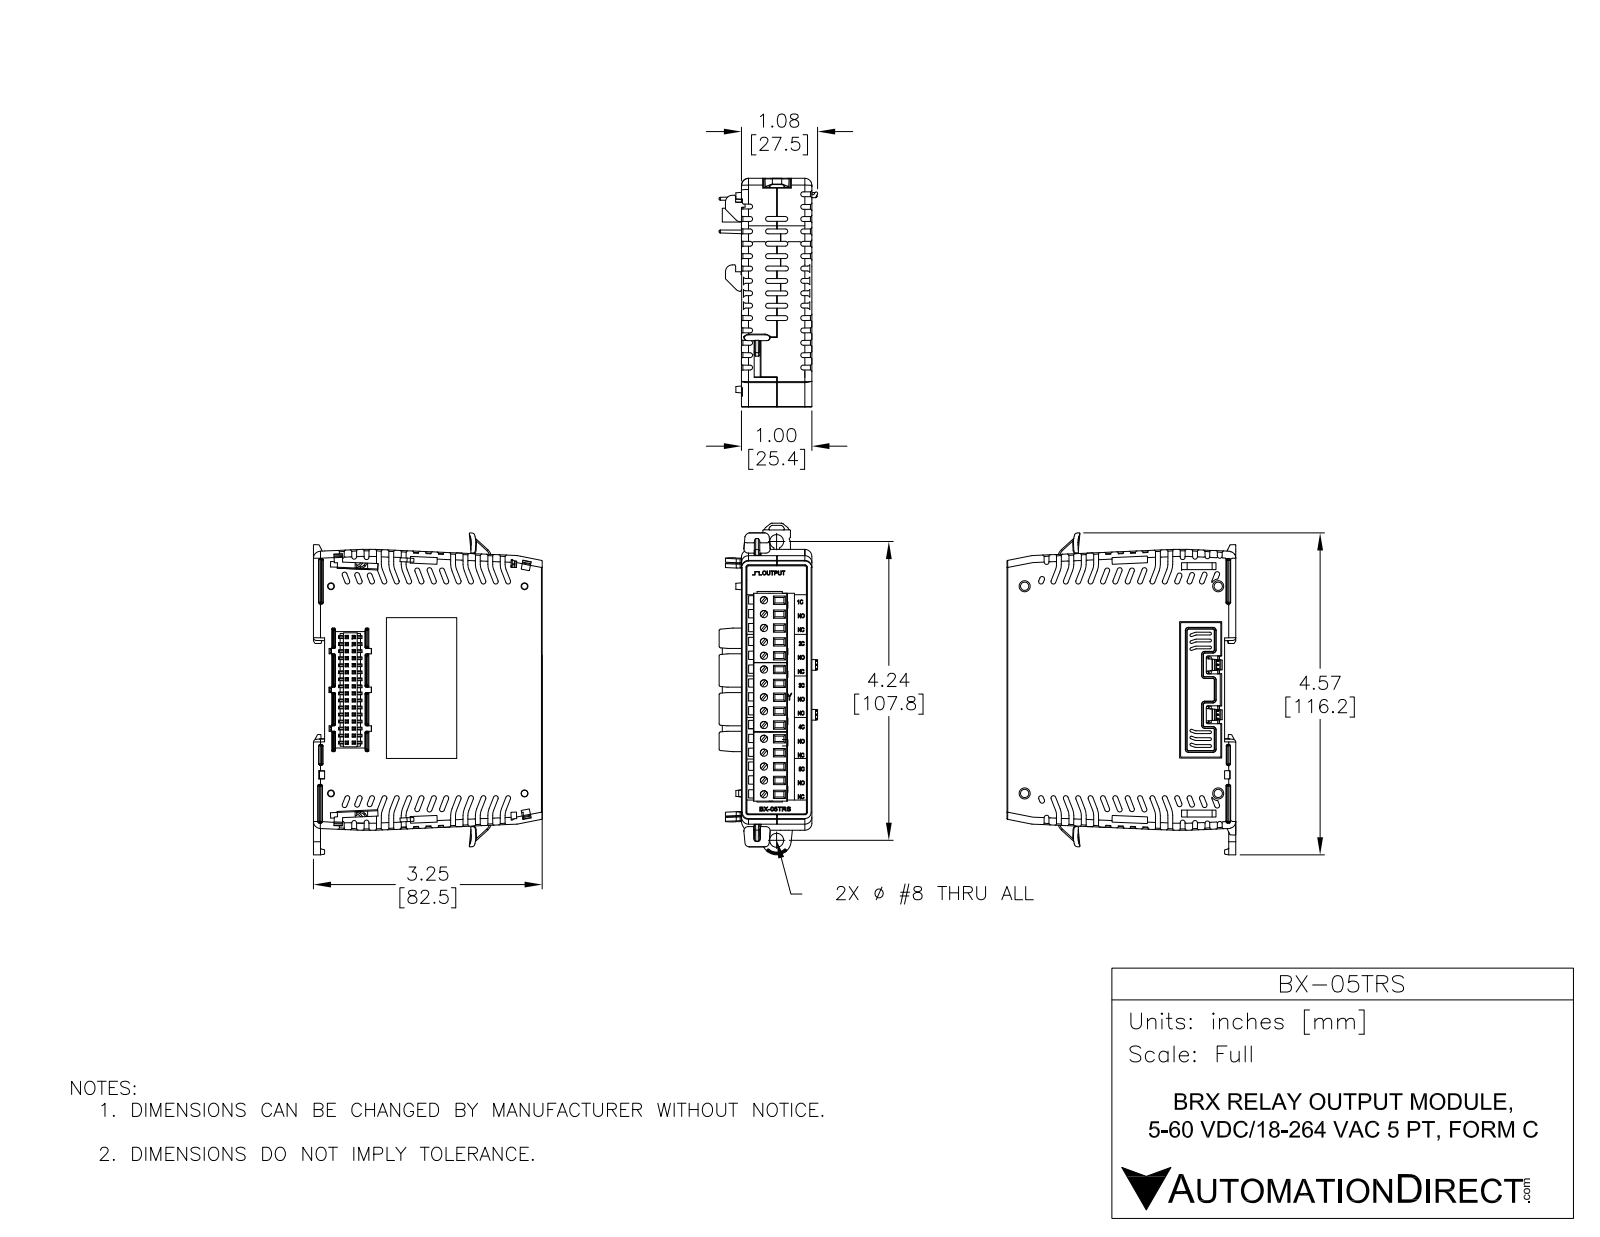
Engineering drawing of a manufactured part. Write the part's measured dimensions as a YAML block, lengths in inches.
part_name: "BX-05TRS"
step_written_by: "SolidWorks 2017 (AUTOMOTIVE_DESIGN)"
units: inches
bodies: {solids: 8, faces: 3817, planar: 2680, cylindrical: 573, other: 564}
overall_size: [4.586, 3.311, 1.402]
volume: 11.6
surface_area: 73.69
round_holes:
  - {diameter: 0.047, count: 2}
  - {diameter: 0.065, count: 2}
  - {diameter: 0.118, count: 2}
  - {diameter: 0.118, count: 2}
  - {diameter: 0.199, count: 1}
round_bosses_or_shafts:
  - {diameter: 0.062, count: 2}
  - {diameter: 0.059, count: 2}
partial_cylinders:
  - {radius: 0.005, count: 102}
  - {radius: 0.01, count: 47}
  - {radius: 0.02, count: 34}
  - {radius: 0.005, count: 24}
  - {radius: 0.008, count: 21}
  - {radius: 0.122, count: 15}
  - {radius: 0.117, count: 14}
  - {radius: 0.039, count: 13}
face_to_face_distances: [1, 3.211, 3.22, 0.1, 0.475, 3.221, 0.157, 3.053, 3.063, 3.063]
hole_center_spacings: [0.1, 0.824, 0.919, 1.3, 2.093, 2.193, 2.585, 2.617]
